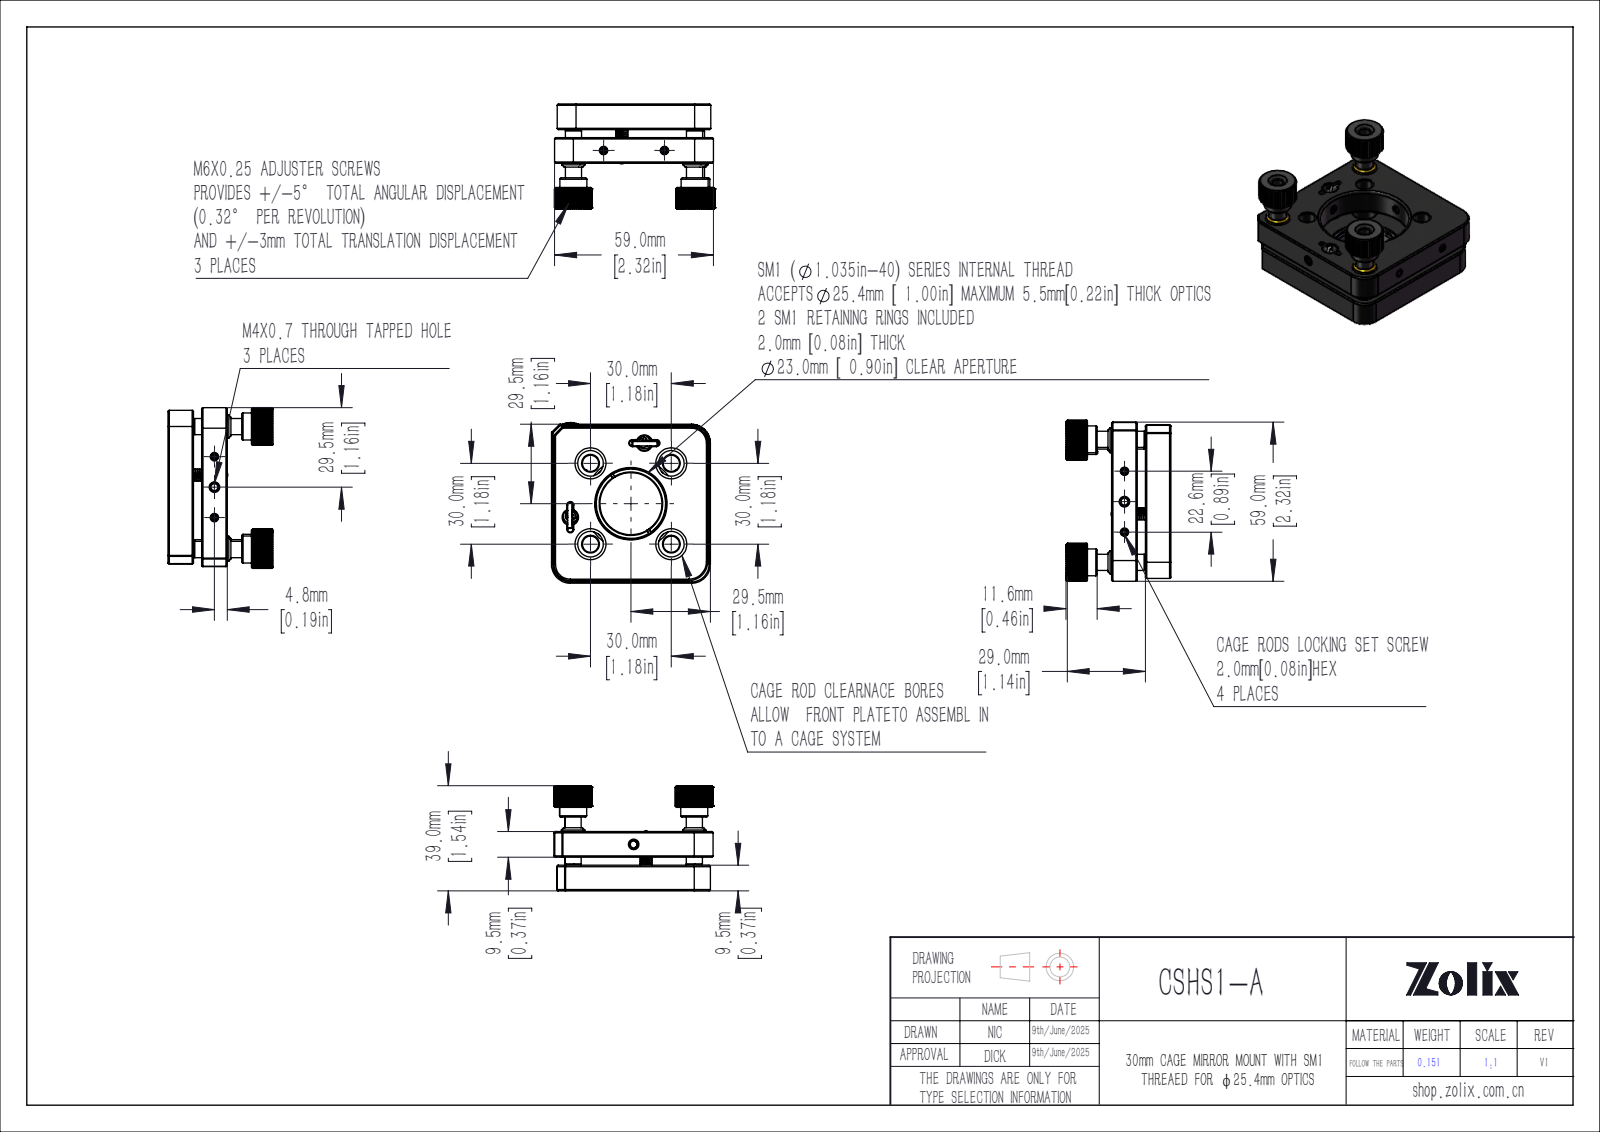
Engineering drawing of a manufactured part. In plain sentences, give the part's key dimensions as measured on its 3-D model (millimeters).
The part is named "CSHS1-A". Its 3-D file was written by "SolidWorks 2020 (CONFIG_CONTROL_DESIGN)". It is 26 solids with 1835 faces: 795 planar, 680 cylindrical and 360 other. Overall it measures 59.64 by 59 by 38.99 millimeters. Its volume is 50 290 cubic millimeters and its surface area 28 351 square millimeters. Round holes: 7 of diameter 6, 4 of diameter 5.5, 4 of diameter 9.5, 3 of diameter 1.95, 3 of diameter 3.3, 3 of diameter 4, 3 of diameter 4.78, 3 of diameter 6.1, 3 of diameter 8.6, 3 of diameter 9.4, 2 of diameter 2.5, 1 of diameter 3. Round bosses or shafts: 4 of diameter 1.6, 3 of diameter 10, 3 of diameter 9.15, 3 of diameter 8.12, 2 of diameter 3, 1 of diameter 26.29. Partial cylindrical surfaces (rounded edges, fillets, slot ends): 28 of radius 0.5, 8 of radius 1, 5 of radius 7, 4 of radius 0.75, 2 of radius 6, 1 of radius 1.5. The main face-to-face distances are 9.5, 12.5, 3, 22, 1, 58, 57, 0.97, 58.97, 57.97. The hole center spacings are 21.21, 30, 38.24, 0.64, 10.61, 11.3, 12.5, 17.5.
